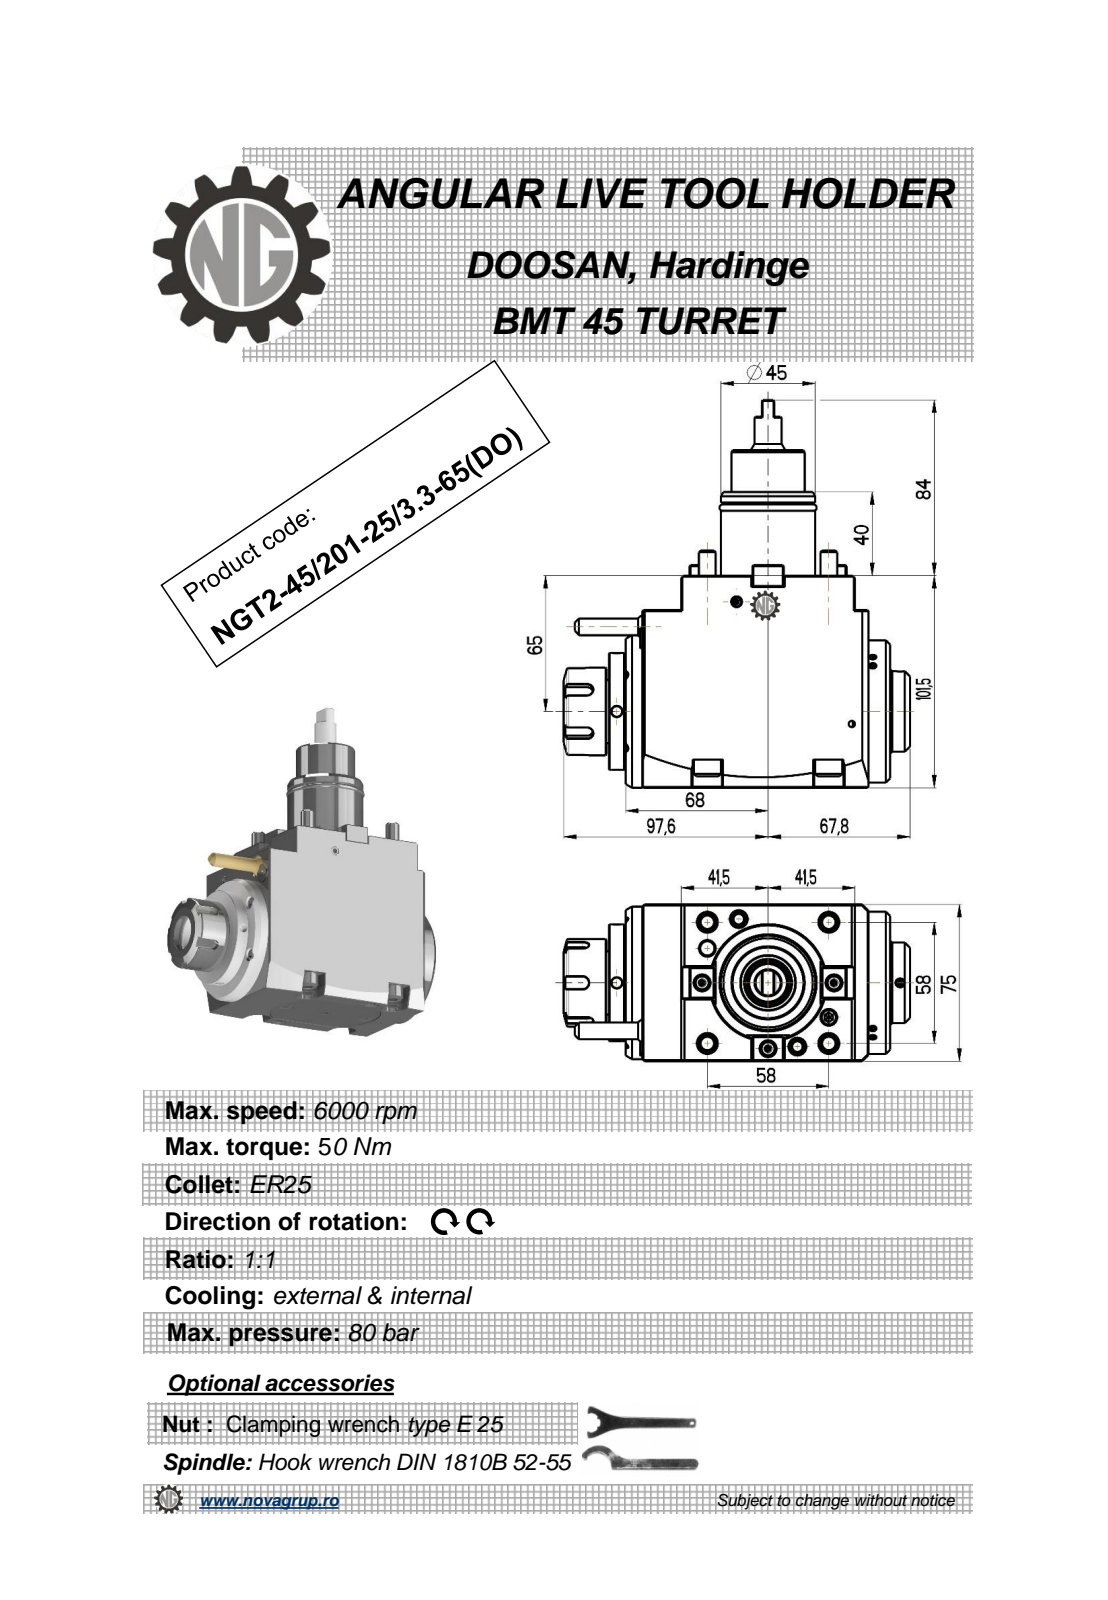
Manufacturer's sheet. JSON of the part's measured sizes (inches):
{"part_name": "NGT2_45_201_25_3_3_65_DO", "step_written_by": "PRO/ENGINEER BY PARAMETRIC TECHNOLOGY CORPORATION, 2010280 (CONFIG_CONTROL_DESIGN)", "units": "inches", "bodies": {"solids": 2, "faces": 483, "planar": 230, "cylindrical": 114, "other": 139}, "overall_size": [7.303, 6.512, 2.953], "volume_in3": 60.86, "surface_area_in2": 125.8, "round_holes": [[0.197, 3], [0.268, 2], [0.118, 1], [0.472, 1], [0.799, 1]], "round_bosses_or_shafts": [[0.512, 5], [0.315, 5], [2.874, 1], [2.677, 1], [2.205, 1], [1.772, 1], [1.709, 1], [1.654, 1]], "partial_cylinders_radius": [[0.01, 20], [0.008, 6], [0.118, 5], [0.276, 4], [0.031, 2], [21.654, 2]], "face_to_face_distances": [2.953, 3.996, 0.315, 4.567, 4.972, 0.406, 3.346, 4.252, 0.65, 4.657], "hole_center_spacings": [1.822, 1.834, 2.627, 4.039]}
